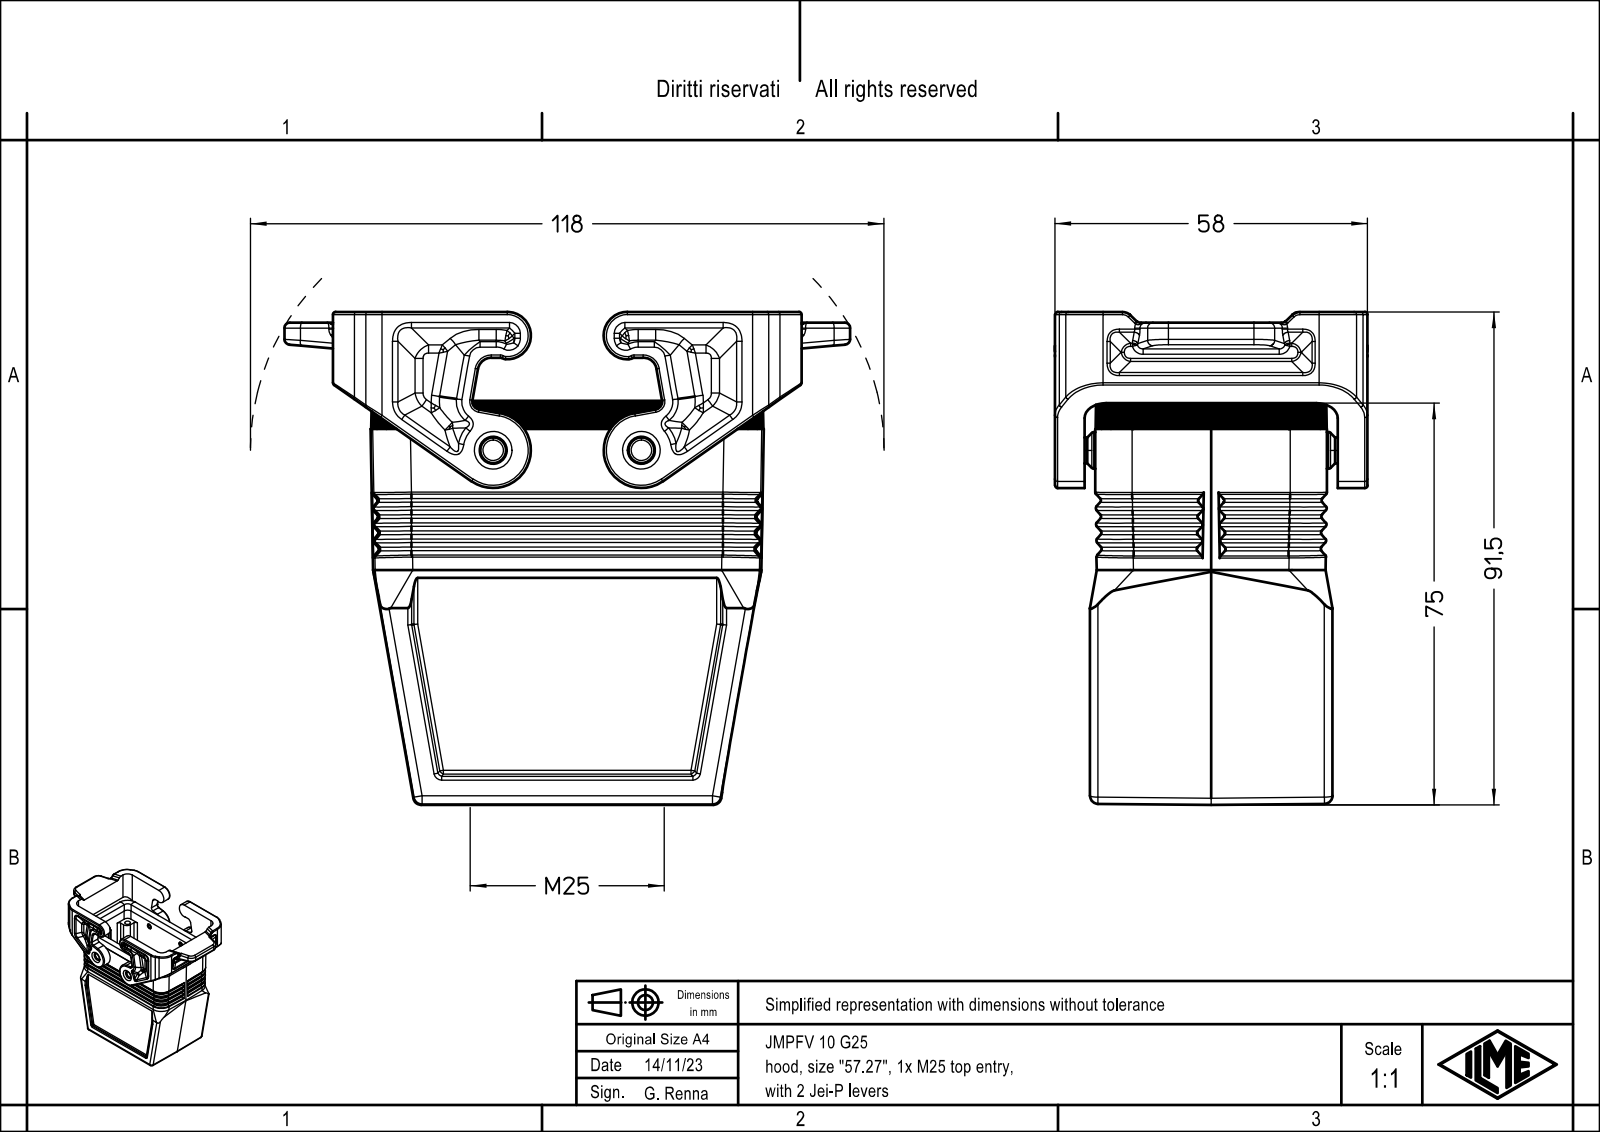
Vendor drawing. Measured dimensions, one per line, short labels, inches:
name: JMPFV 10 G25
written by: Creo Elements/Direct Modeling 20.1B 02-Apr-2019 (C) Parametric Technology GmbH (AUTOMOTIVE_DESIGN)
unit: in
bodies: 1 solid, 1097 faces (270 planar, 349 cylindrical, 478 other)
size: 4.134 × 3.6 × 2.287
volume: 5.977 in³; area: 74.55 in²
holes: 4× ⌀0.118, 4× ⌀0.138, 2× ⌀0.189, 1× ⌀0.929
bosses: 2× ⌀0.268
rounds: 69× R0.02, 56× R0.039, 34× R0.118, 28× R0.059, 20× R0.079, 15× R0.013, 14× R0.276, 12× R0.157
face distances: 1.545, 0.079, 0.148, 0.226, 0.039, 1.772, 1.624, 1.693, 0.187, 1.585
hole spacings: 1.242, 1.063, 2.244, 2.483, 1.083
